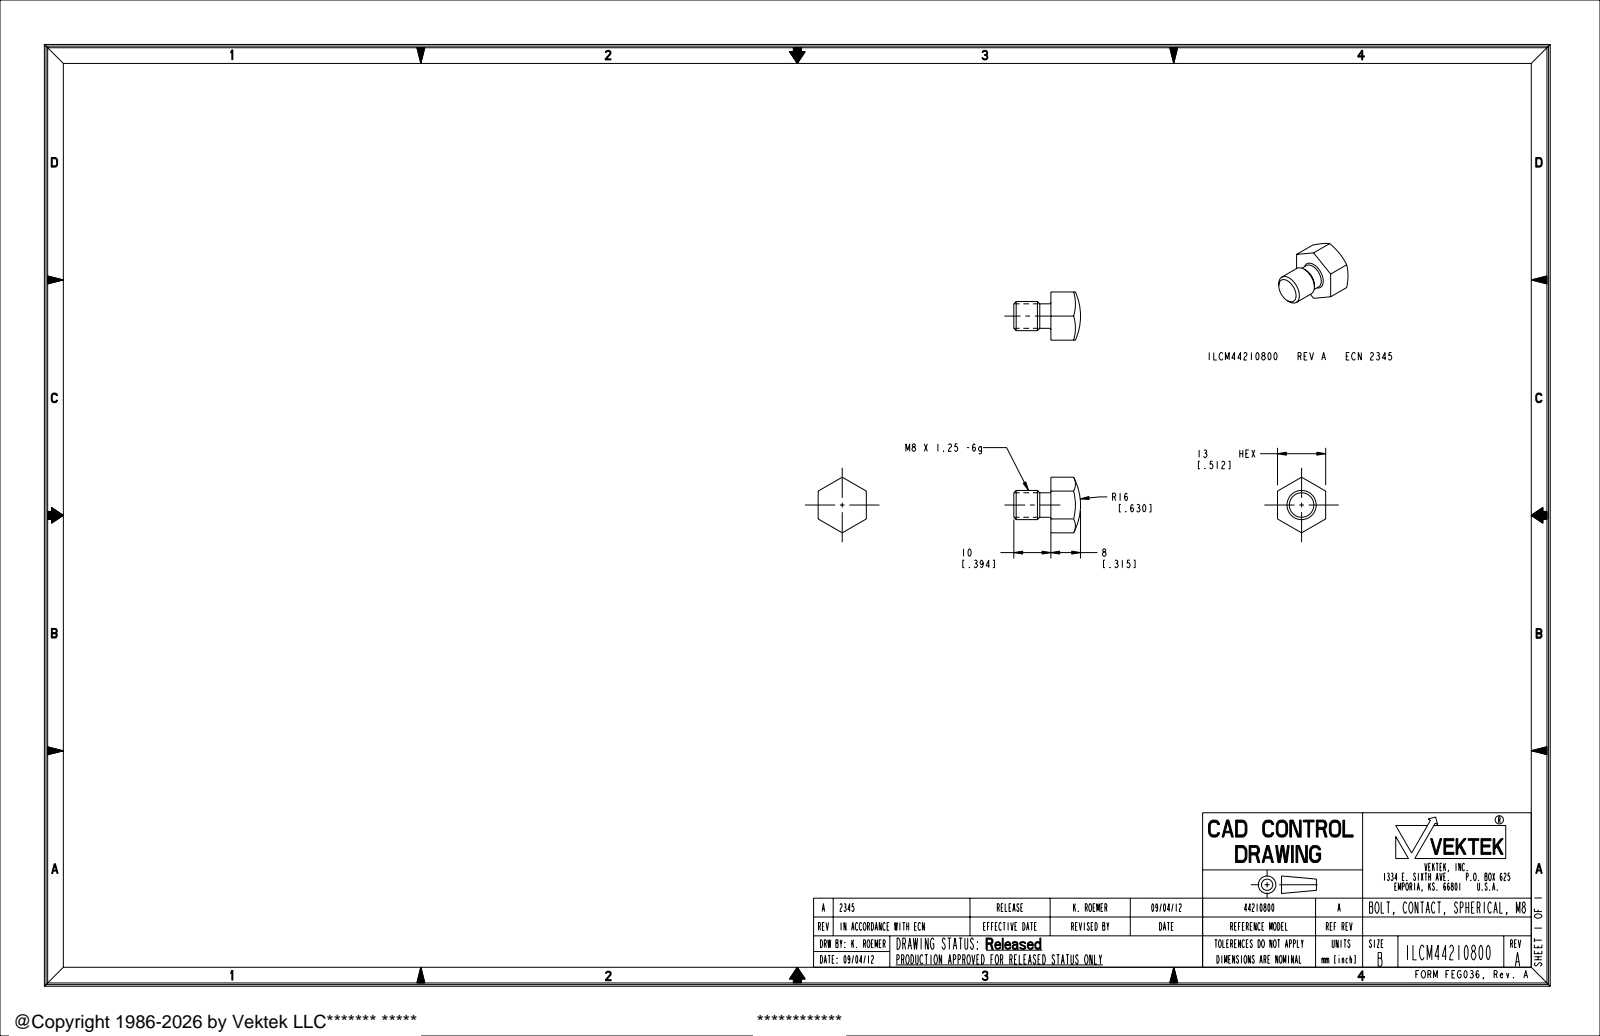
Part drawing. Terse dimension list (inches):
name: ILCM44210800
written by: PRO/ENGINEER BY PARAMETRIC TECHNOLOGY CORPORATION, 2007460 (AUTOMOTIVE_DESIGN_CC2)
unit: in
bodies: 1 solid, 22 faces (8 planar, 6 cylindrical, 8 other)
size: 0.709 × 0.591 × 0.512
volume: 0.091 in³; area: 1.52 in²
bosses: 1× ⌀0.31, 1× ⌀0.26
face distances: 0.512, 0.394
